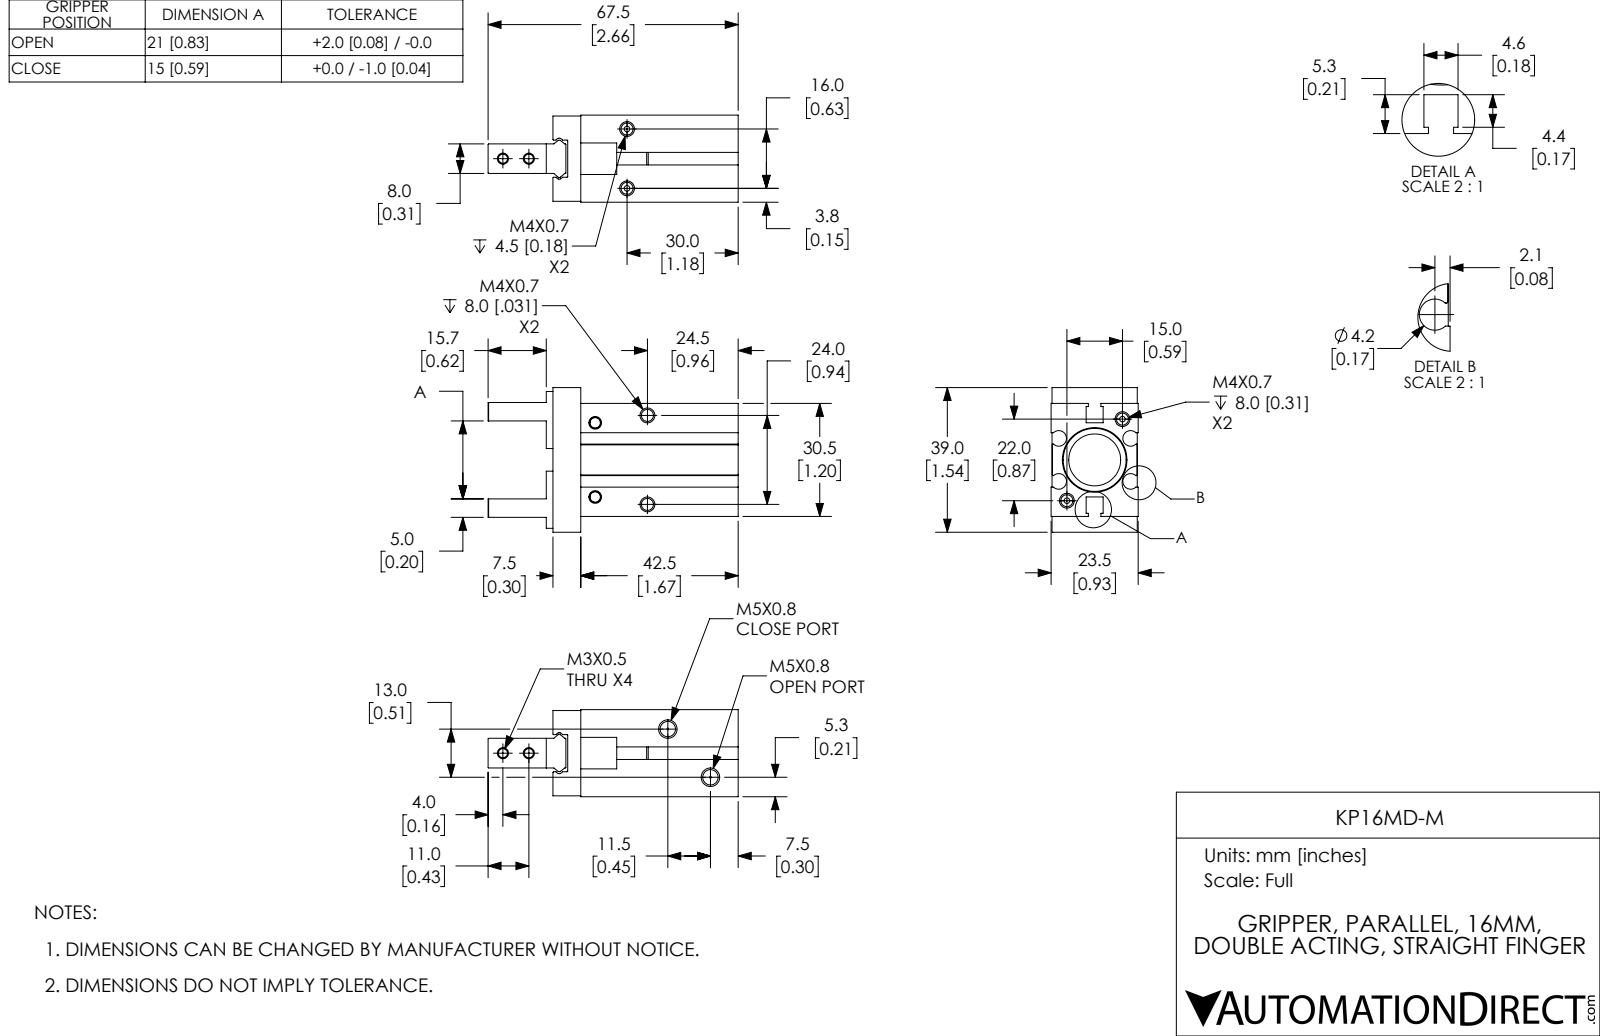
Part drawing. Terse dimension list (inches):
name: KP16MD-M-1; KP16MD-M; KP16MD-M-2; KP16MD-M-3
written by: SolidWorks 2017 (CONFIG_CONTROL_DESIGN)
unit: in
bodies: 3 solids, 244 faces (116 planar, 66 cylindrical, 62 other)
size: 2.657 × 1.535 × 0.925
volume: 1.842 in³; area: 20.74 in²
holes: 6× ⌀0.128, 2× ⌀0.02, 2× ⌀0.097, 2× ⌀0.158, 2× ⌀0.163, 1× ⌀0.551, 1× ⌀0.669
rounds: 10× R0.008, 4× R0.083, 2× R0.016, 2× R0.02, 2× R0.039
face distances: 0.295, 0.62, 0.157, 1.201, 0.913, 0.618, 0.925, 0.283, 0.138, 0.63
hole spacings: 0.524, 1.09, 1.356, 0.276, 0.437, 0.63, 0.683, 0.717
